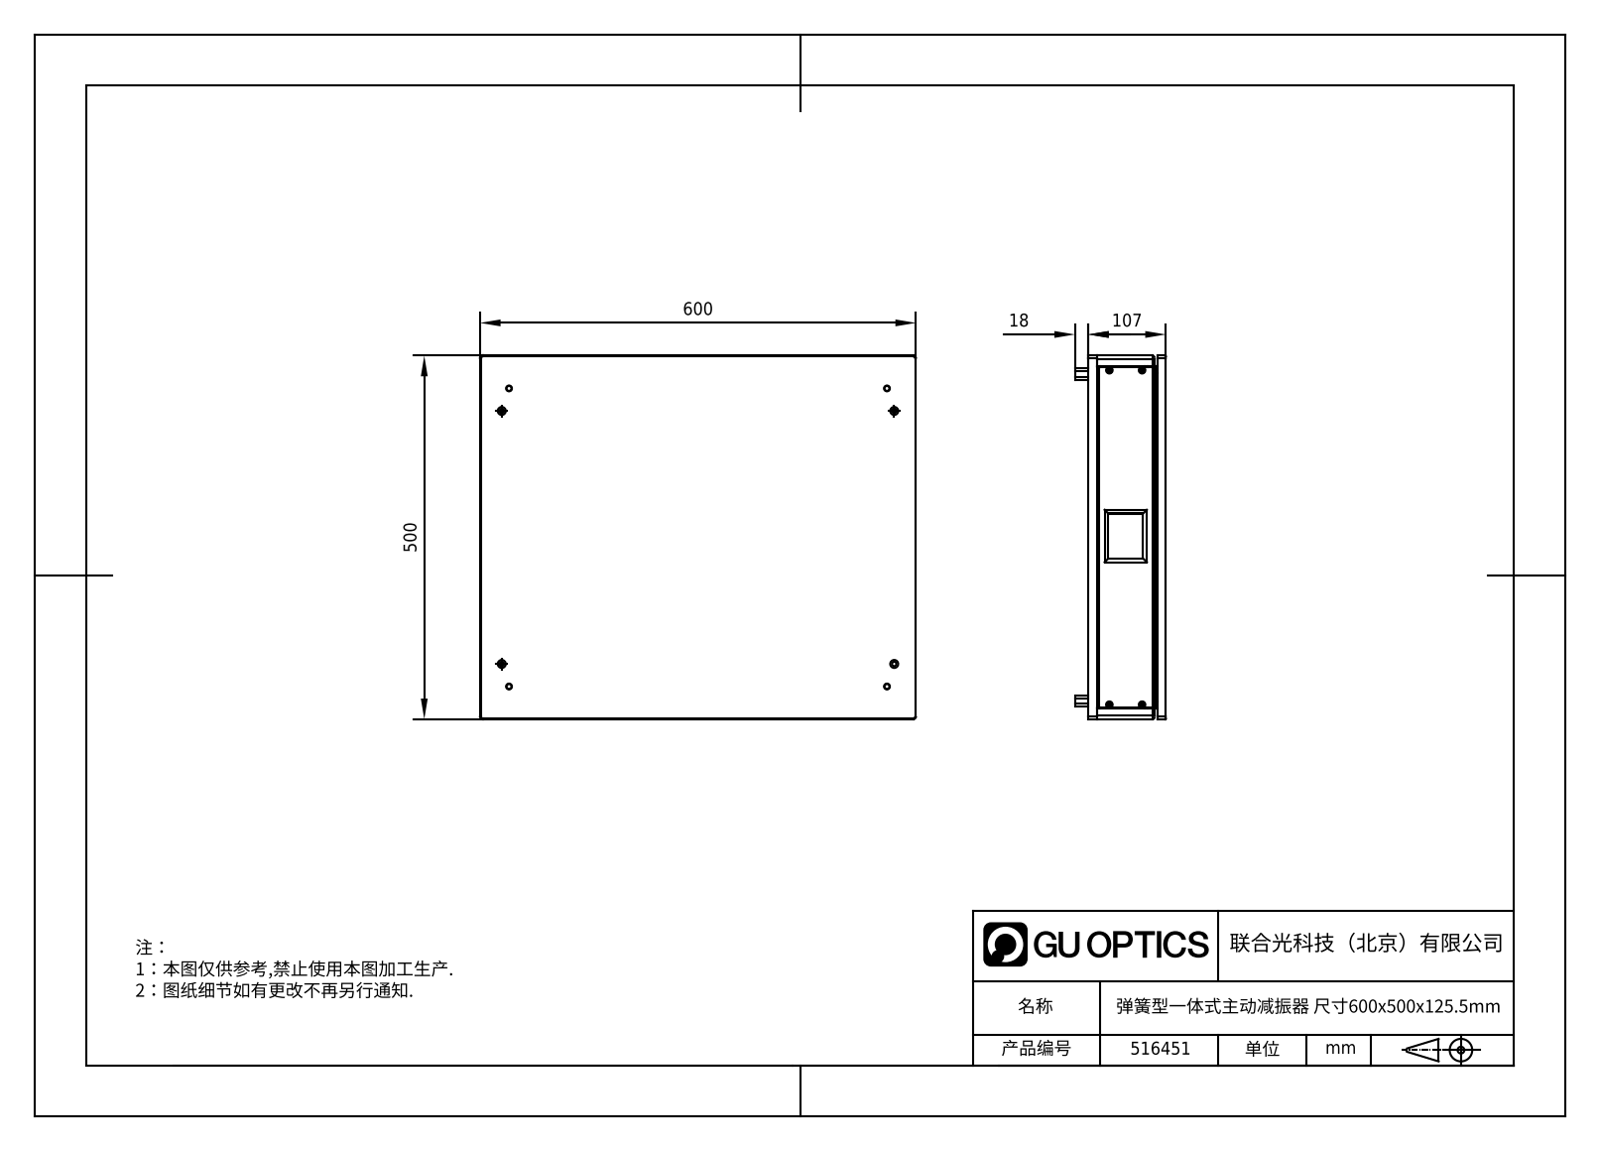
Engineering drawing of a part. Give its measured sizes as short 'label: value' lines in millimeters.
name: 516451
written by: SolidWorks 2020 (CONFIG_CONTROL_DESIGN)
unit: mm
bodies: 37 solids, 1408 faces (695 planar, 568 cylindrical, 145 other)
size: 600 × 500 × 125
volume: 11 140 000 mm³; area: 2 833 000 mm²
holes: 70× ⌀8, 50× ⌀3.3, 38× ⌀4.5, 32× ⌀4.3, 26× ⌀5.2, 24× ⌀2.5, 18× ⌀4.2, 12× ⌀10, 8× ⌀5.5, 8× ⌀6.8, 4× ⌀5.1, 4× ⌀6.1
bosses: 9× ⌀1, 8× ⌀7.53, 8× ⌀4, 4× ⌀8
rounds: 26× R2, 22× R1, 18× R5, 14× R3, 8× R0.5, 8× R8, 6× R0.74, 6× R2.74
face distances: 12, 95, 82, 13, 1, 83, 94, 107, 25, 70
hole spacings: 32, 12.73, 45, 211.99, 410, 471.09, 571.07, 740.19
